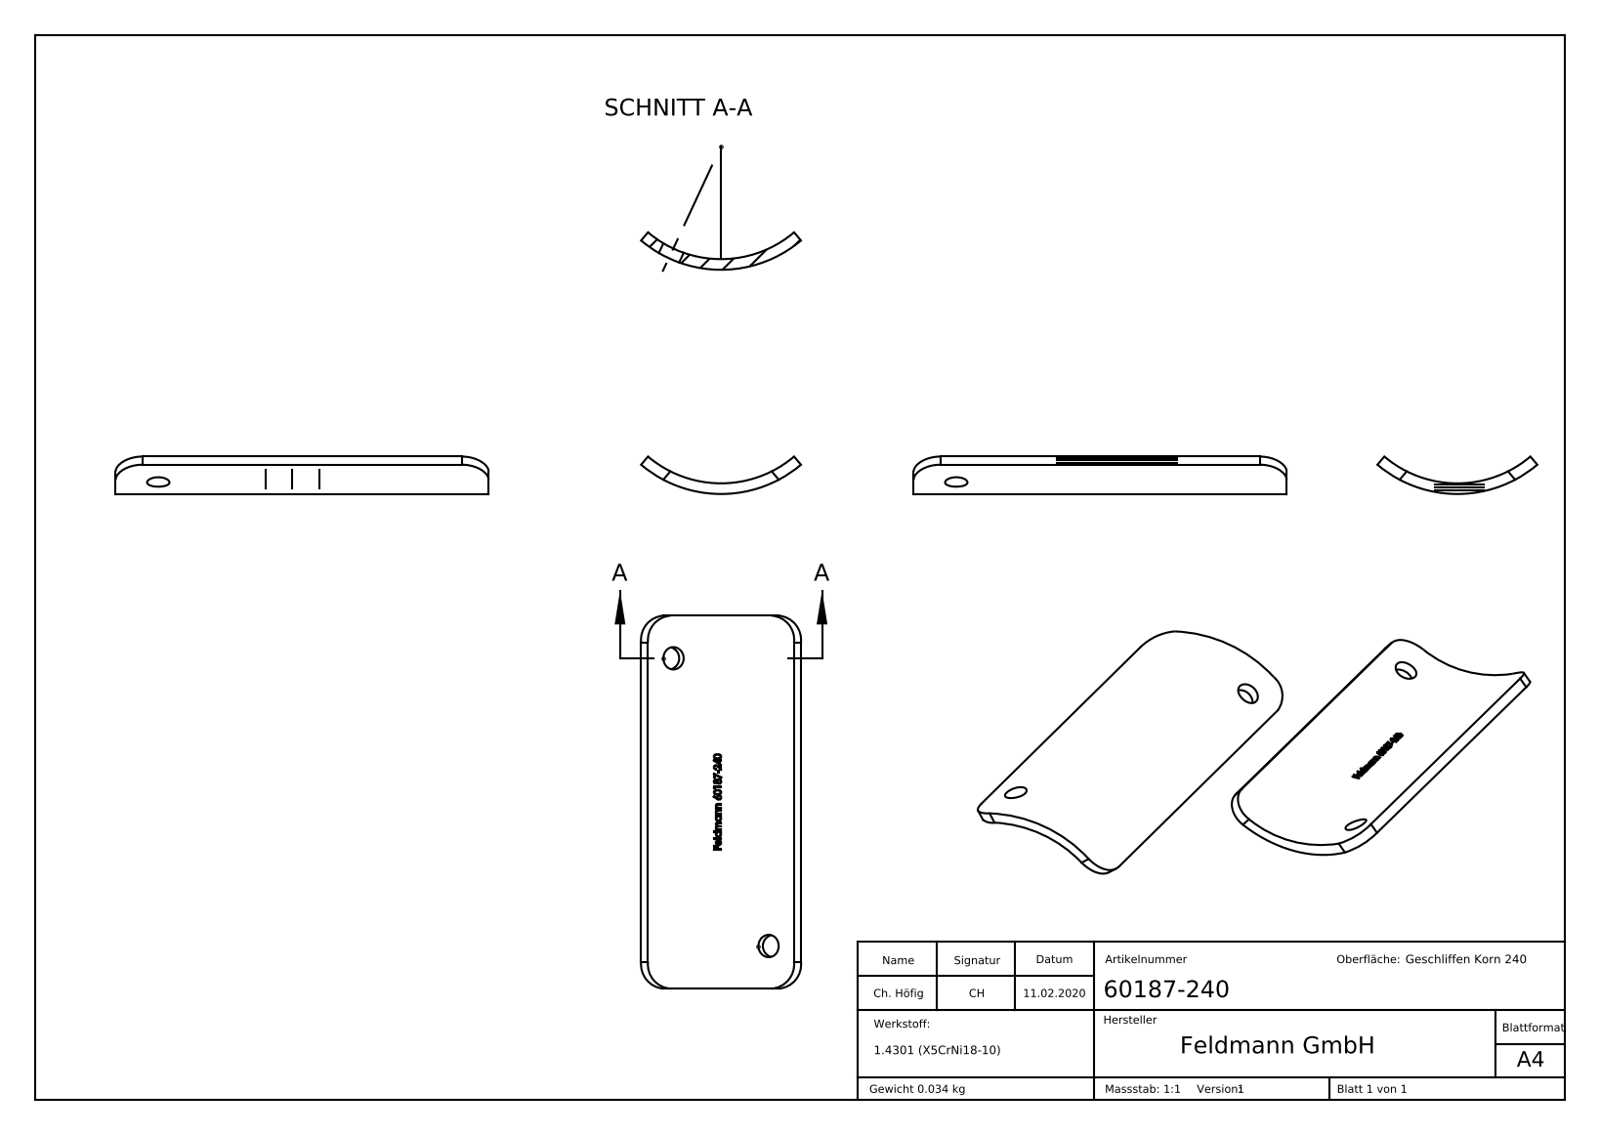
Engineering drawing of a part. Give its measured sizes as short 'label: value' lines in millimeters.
name: 60187-240
written by: SolidWorks 2015 (CONFIG_CONTROL_DESIGN)
unit: mm
bodies: 1 solid, 228 faces (96 planar, 34 cylindrical, 98 other)
size: 70 × 30 × 7.03
volume: 4 271 mm³; area: 4 722 mm²
holes: 2× ⌀4.2
rounds: 4× R5, 1× R21.2, 1× R21.3, 1× R23.2
face distances: 70, 0.39, 2.97, 11.73, 1.32, 14.62, 8.46, 0.88, 3.27, 0.44
